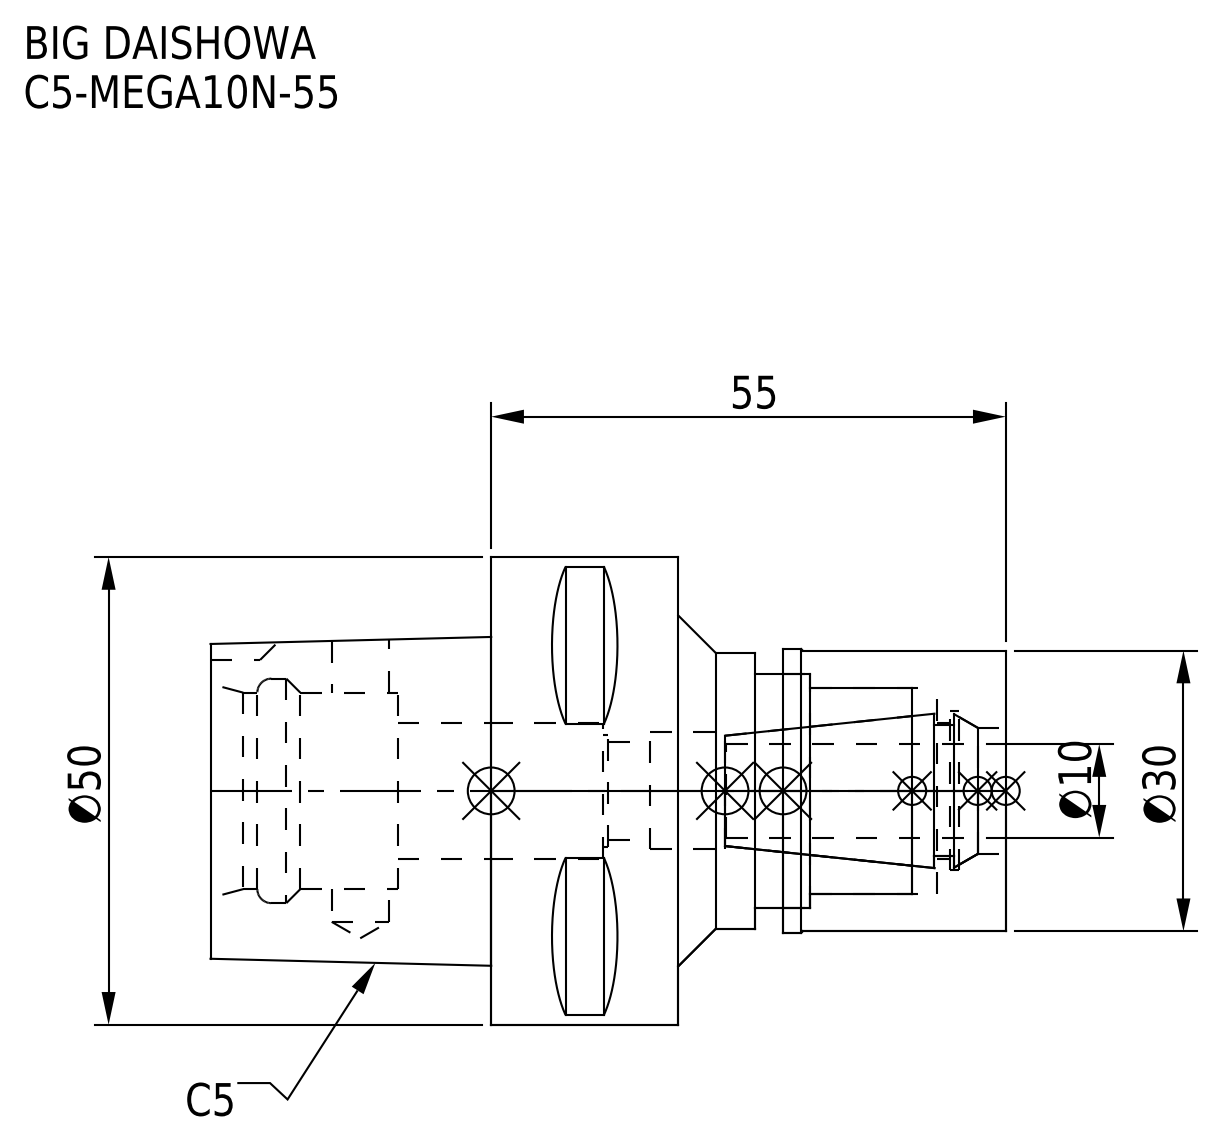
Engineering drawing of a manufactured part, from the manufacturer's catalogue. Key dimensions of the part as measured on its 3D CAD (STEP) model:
Part name (STEP PRODUCT): C5-MEGA10N-55-100.stp; MGN10_1.stp; C5-MEGA10N-55_1.stp; C5-MEGA10N-55-100-FreeParts (+3 more)
STEP written by: SolidWorks 2019 (CONFIG_CONTROL_DESIGN)
Units: millimetres
Bodies: 2 solids, 98 faces (39 planar, 41 cylindrical, 18 other)
Overall size (bounding box): 85 × 50 × 50
Volume: 72 515 mm³ · Surface area: 20 852 mm²
Round holes (diameter × count): ⌀6.1 ×1, ⌀10.4 ×1, ⌀12 ×1, ⌀12.5 ×1, ⌀13.5 ×1, ⌀14.5 ×1, ⌀17 ×1, ⌀21 ×1, ⌀22 ×1, ⌀24 ×1, ⌀25 ×1
Round bosses / shafts (diameter × count): ⌀50 ×1, ⌀30.3 ×1, ⌀30 ×1, ⌀29.5 ×1
Partial cylindrical surfaces — rounded edges, fillets, slot ends (radius × count): R4 ×1
Main face-to-face distances: 20, 55, 30, 35, 50, 85, 10, 11.2, 3, 23.8
